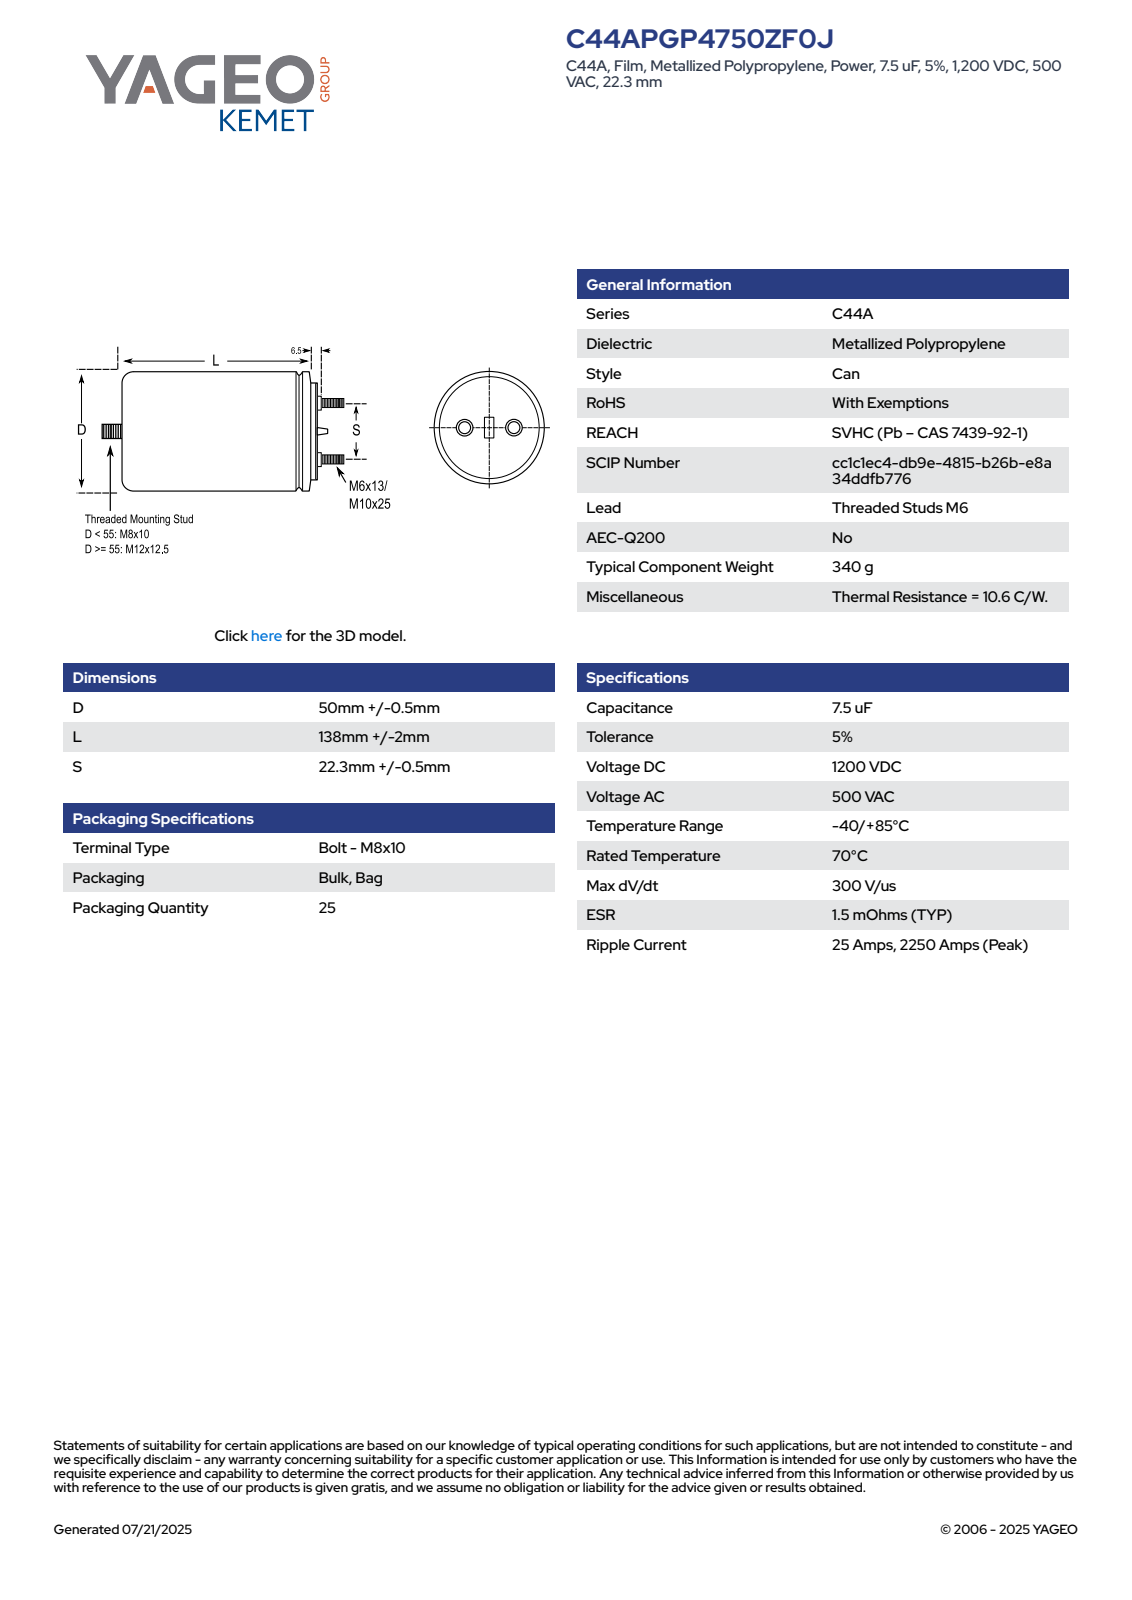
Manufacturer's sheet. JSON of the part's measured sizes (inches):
{"part_name": "CFP_C44A_50X138_D50.5L140S22.3", "step_written_by": "SolidWorks 2014 (AUTOMOTIVE_DESIGN)", "units": "inches", "bodies": {"solids": 1, "faces": 102, "planar": 29, "cylindrical": 34, "other": 39}, "overall_size": [6.673, 1.988, 1.988], "volume_in3": 17.42, "surface_area_in2": 42.21, "round_bosses_or_shafts": [[0.354, 2], [0.236, 2], [1.988, 1], [1.559, 1], [0.315, 1]], "partial_cylinders_radius": [[0.994, 1]], "face_to_face_distances": [5.709, 5.768, 0.059, 6.28, 0.571, 0.512, 0.394, 6.102, 6.161, 6.673]}
